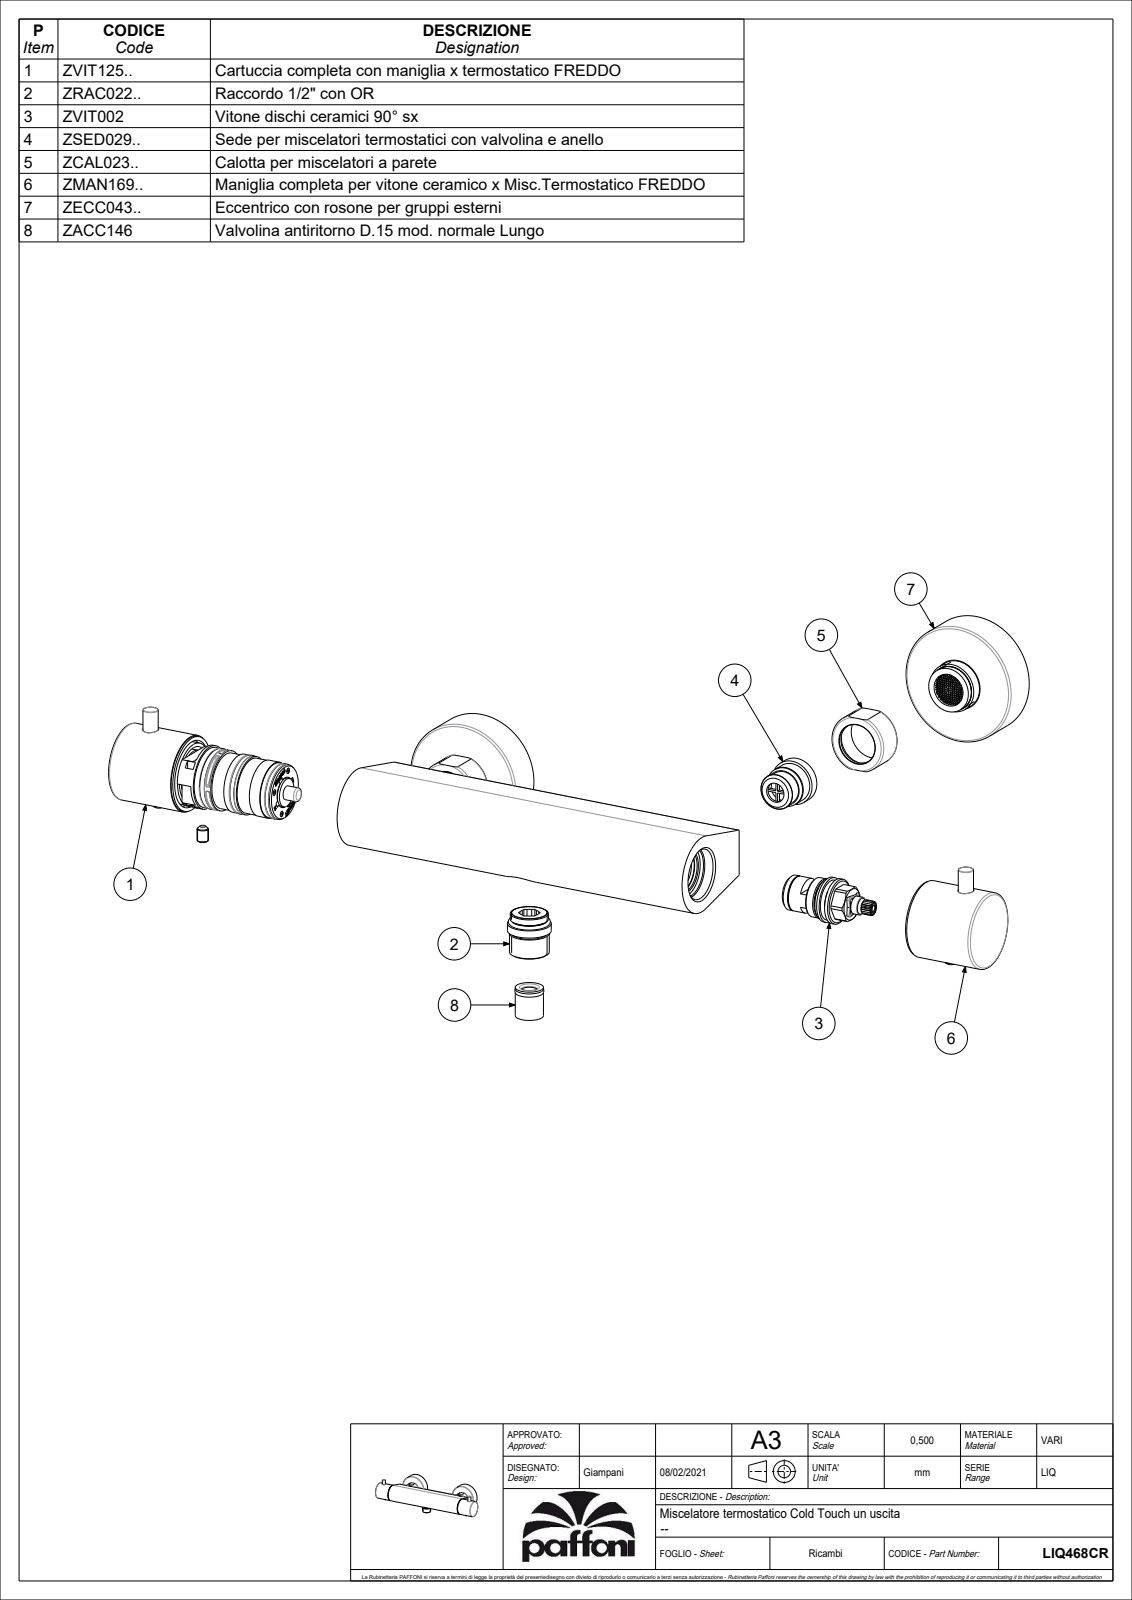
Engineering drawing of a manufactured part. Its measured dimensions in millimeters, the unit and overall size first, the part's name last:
Units: millimetres
Overall size (bounding box): 287.52 × 100.46 × 64.75
Round holes (diameter × count): ⌀1.8 ×4, ⌀4 ×4, ⌀8.5 ×3, ⌀12.4 ×3, ⌀15.1 ×3, ⌀2.5 ×2, ⌀3 ×2, ⌀3.25 ×2, ⌀6 ×2, ⌀8.2 ×2, ⌀10.5 ×2, ⌀16 ×2
Round bosses / shafts (diameter × count): ⌀14.8 ×3, ⌀63.5 ×2, ⌀27 ×2, ⌀24 ×2, ⌀21.2 ×2, ⌀15.5 ×2, ⌀8 ×2, ⌀7.6 ×2
Partial cylindrical surfaces — rounded edges, fillets, slot ends (radius × count): R2.17 ×102, R0.5 ×20, R1.18 ×7, R1.75 ×4, R1.9 ×4, R1.68 ×3, R2.17 ×2, R2.96 ×2
Main face-to-face distances: 0.6, 21.1, 20.5, 3, 2.99, 3.16, 3.15, 37, 246, 14.5
Hole centre spacings: 5.96, 150, 7.2, 129.5, 146.48, 153.67, 0.75, 5
Volume: 238 401 mm³ · Surface area: 158 168 mm²
Bodies: 2 solids, 2797 faces (1833 planar, 404 cylindrical, 560 other)
Part name (STEP PRODUCT): LIQ468CR
STEP written by: CREO PARAMETRIC BY PTC INC, 2020044 (CONFIG_CONTROL_DESIGN)
